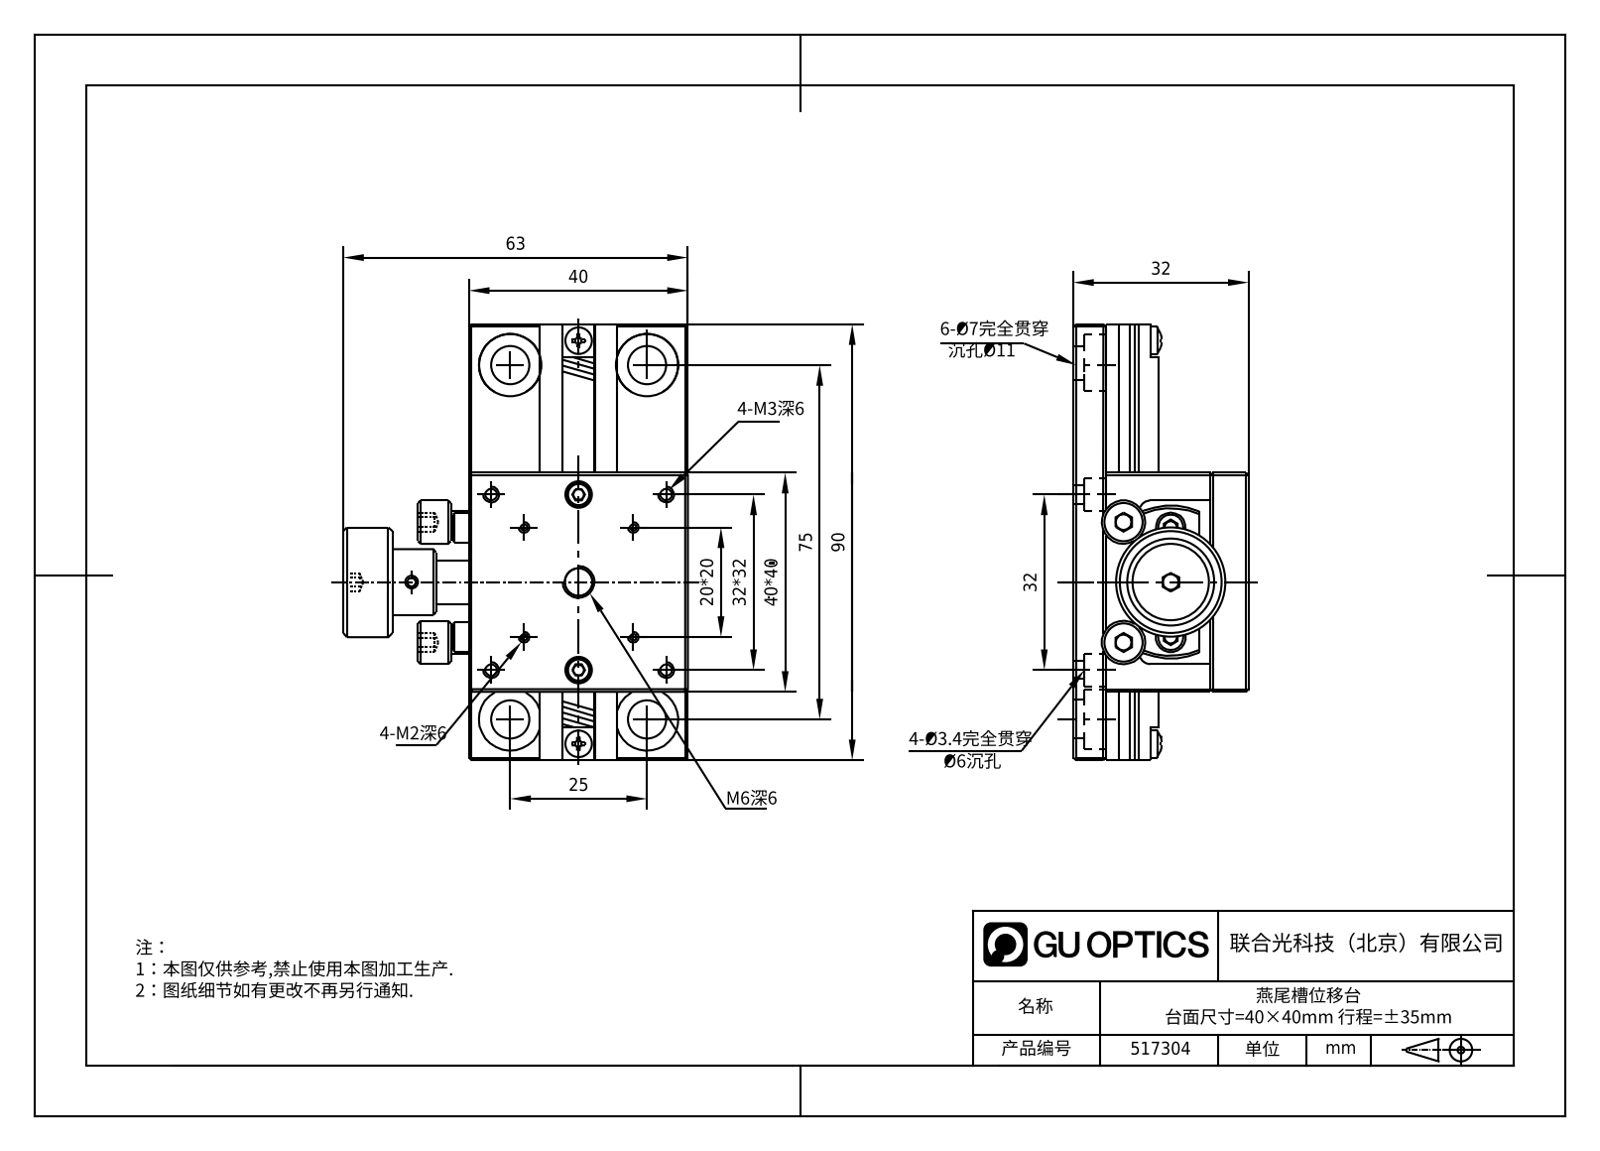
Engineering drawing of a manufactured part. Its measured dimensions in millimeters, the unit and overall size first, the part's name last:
Units: millimetres
Overall size (bounding box): 90 × 63 × 32
Round holes (diameter × count): ⌀3 ×6, ⌀2 ×4, ⌀3.4 ×4, ⌀7 ×4, ⌀11.5 ×4, ⌀2.05 ×3, ⌀2.5 ×2, ⌀5 ×2, ⌀6 ×1, ⌀8 ×1
Round bosses / shafts (diameter × count): ⌀2.5 ×3, ⌀8 ×2, ⌀5 ×2, ⌀4.5 ×2, ⌀4 ×2, ⌀20 ×1, ⌀12 ×1
Partial cylindrical surfaces — rounded edges, fillets, slot ends (radius × count): R0.3 ×8, R2 ×2, R14 ×1
Main face-to-face distances: 6, 25, 19, 40, 26, 32, 7, 13, 20, 17.1
Hole centre spacings: 16, 22.63, 35.78, 11.66, 26.68, 27.86, 32, 8.49
Bodies: 0 solids, 552 faces (465 planar, 56 cylindrical, 31 other)
Part name (STEP PRODUCT): 517304
STEP written by: SolidWorks 2020 (CONFIG_CONTROL_DESIGN)
